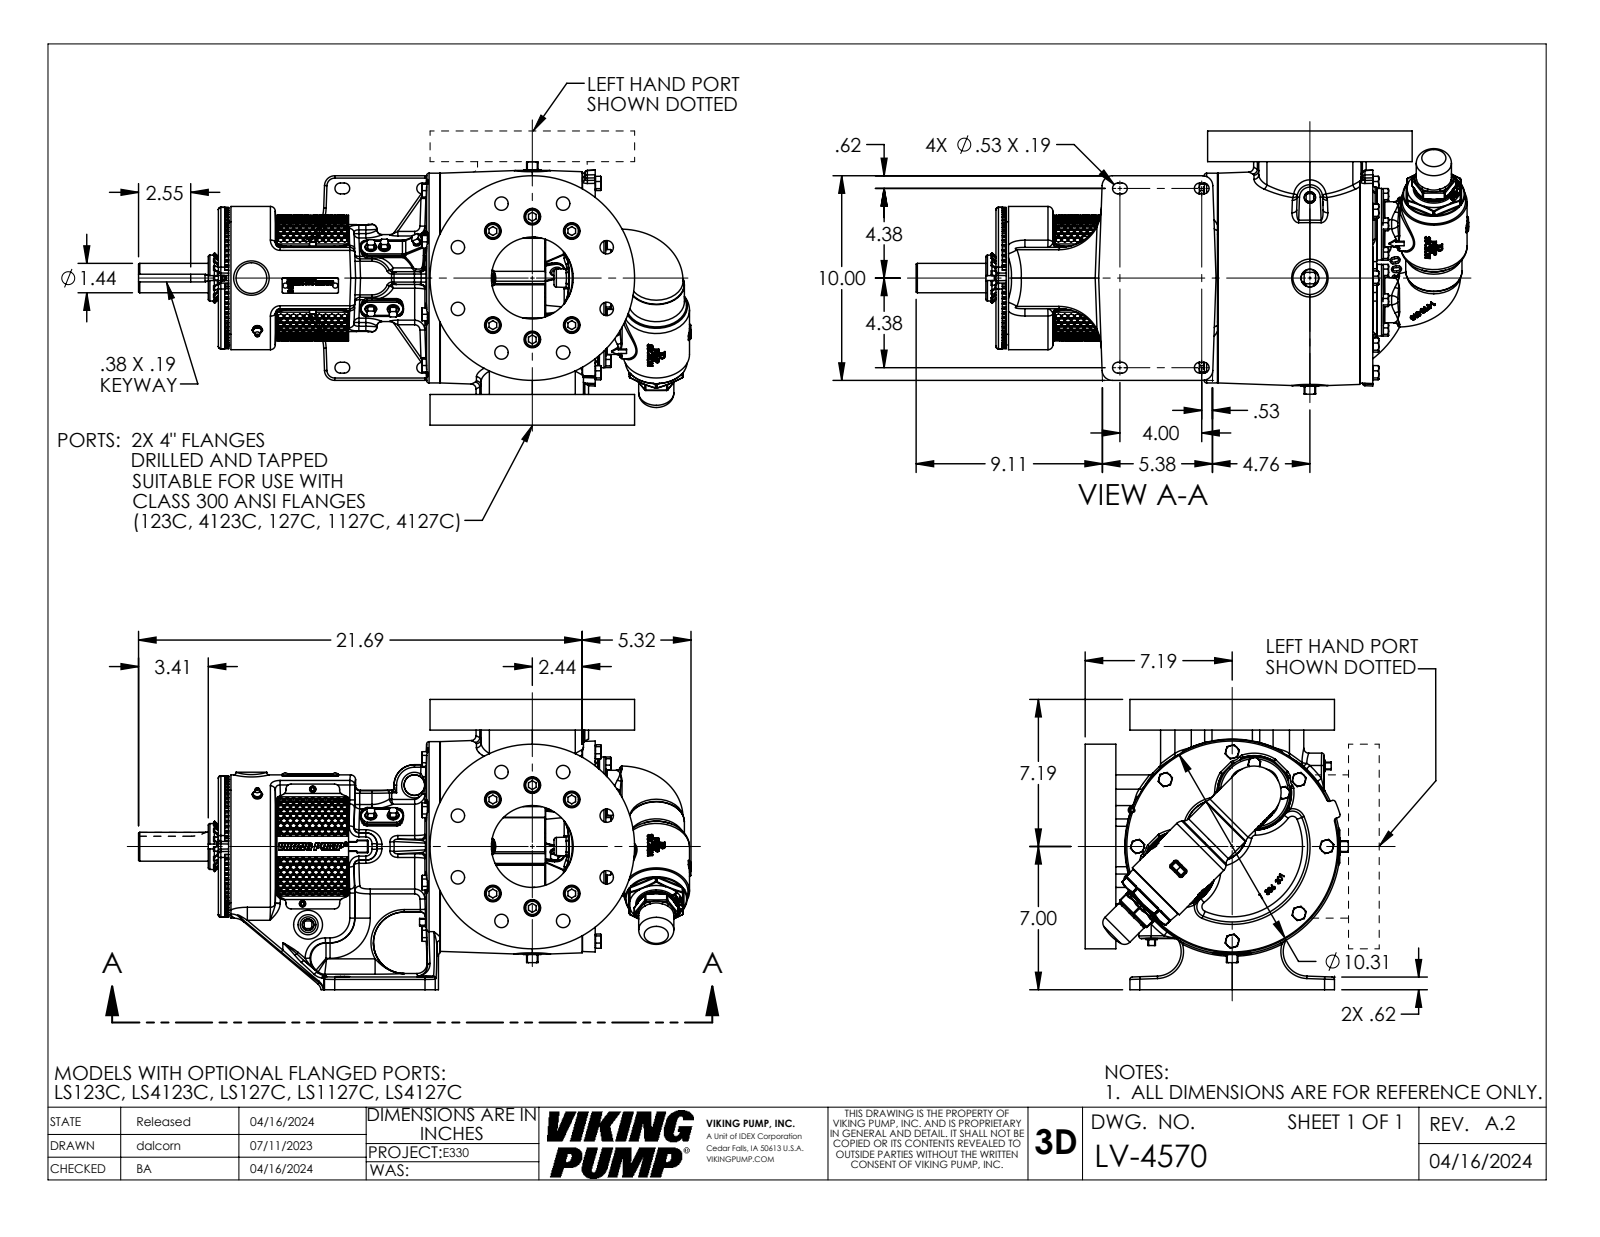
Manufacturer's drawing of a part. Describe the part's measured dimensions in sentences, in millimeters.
The part is named "LV-4570". Its 3-D file was written by "SolidWorks 2022 (AUTOMOTIVE_DESIGN)". It is 1 solid with 5523 faces: 1790 planar, 1095 cylindrical and 2638 other. Overall it measures 686 by 360.4 by 326.7 millimeters. Its volume is 20 980 000 cubic millimeters and its surface area 1 117 000 square millimeters. Round holes: 16 of diameter 16.7, 12 of diameter 14.3, 12 of diameter 20.6, 8 of diameter 27.8, 6 of diameter 5.1, 6 of diameter 6.4, 3 of diameter 4, 2 of diameter 6.8, 2 of diameter 8, 2 of diameter 101.6, 1 of diameter 11.5, 1 of diameter 38.3. Round bosses or shafts: 12 of diameter 19.1, 12 of diameter 12.7, 10 of diameter 15.9, 6 of diameter 15.9, 3 of diameter 88.9, 3 of diameter 11.1, 3 of diameter 7.9, 2 of diameter 254. Partial cylindrical surfaces (rounded edges, fillets, slot ends): 109 of radius 1.6, 81 of radius 3, 74 of radius 1.8, 48 of radius 6.1, 24 of radius 0.8, 19 of radius 1.5, 16 of radius 25.4, 14 of radius 12.7. The main face-to-face distances are 38.1, 322.2, 360.3, 12.7, 455.2, 398.1, 57.2, 90, 308.1, 54.2. The hole center spacings are 76.2, 100, 141.5, 184.8, 34.9, 35.7, 41.6, 47.9.
